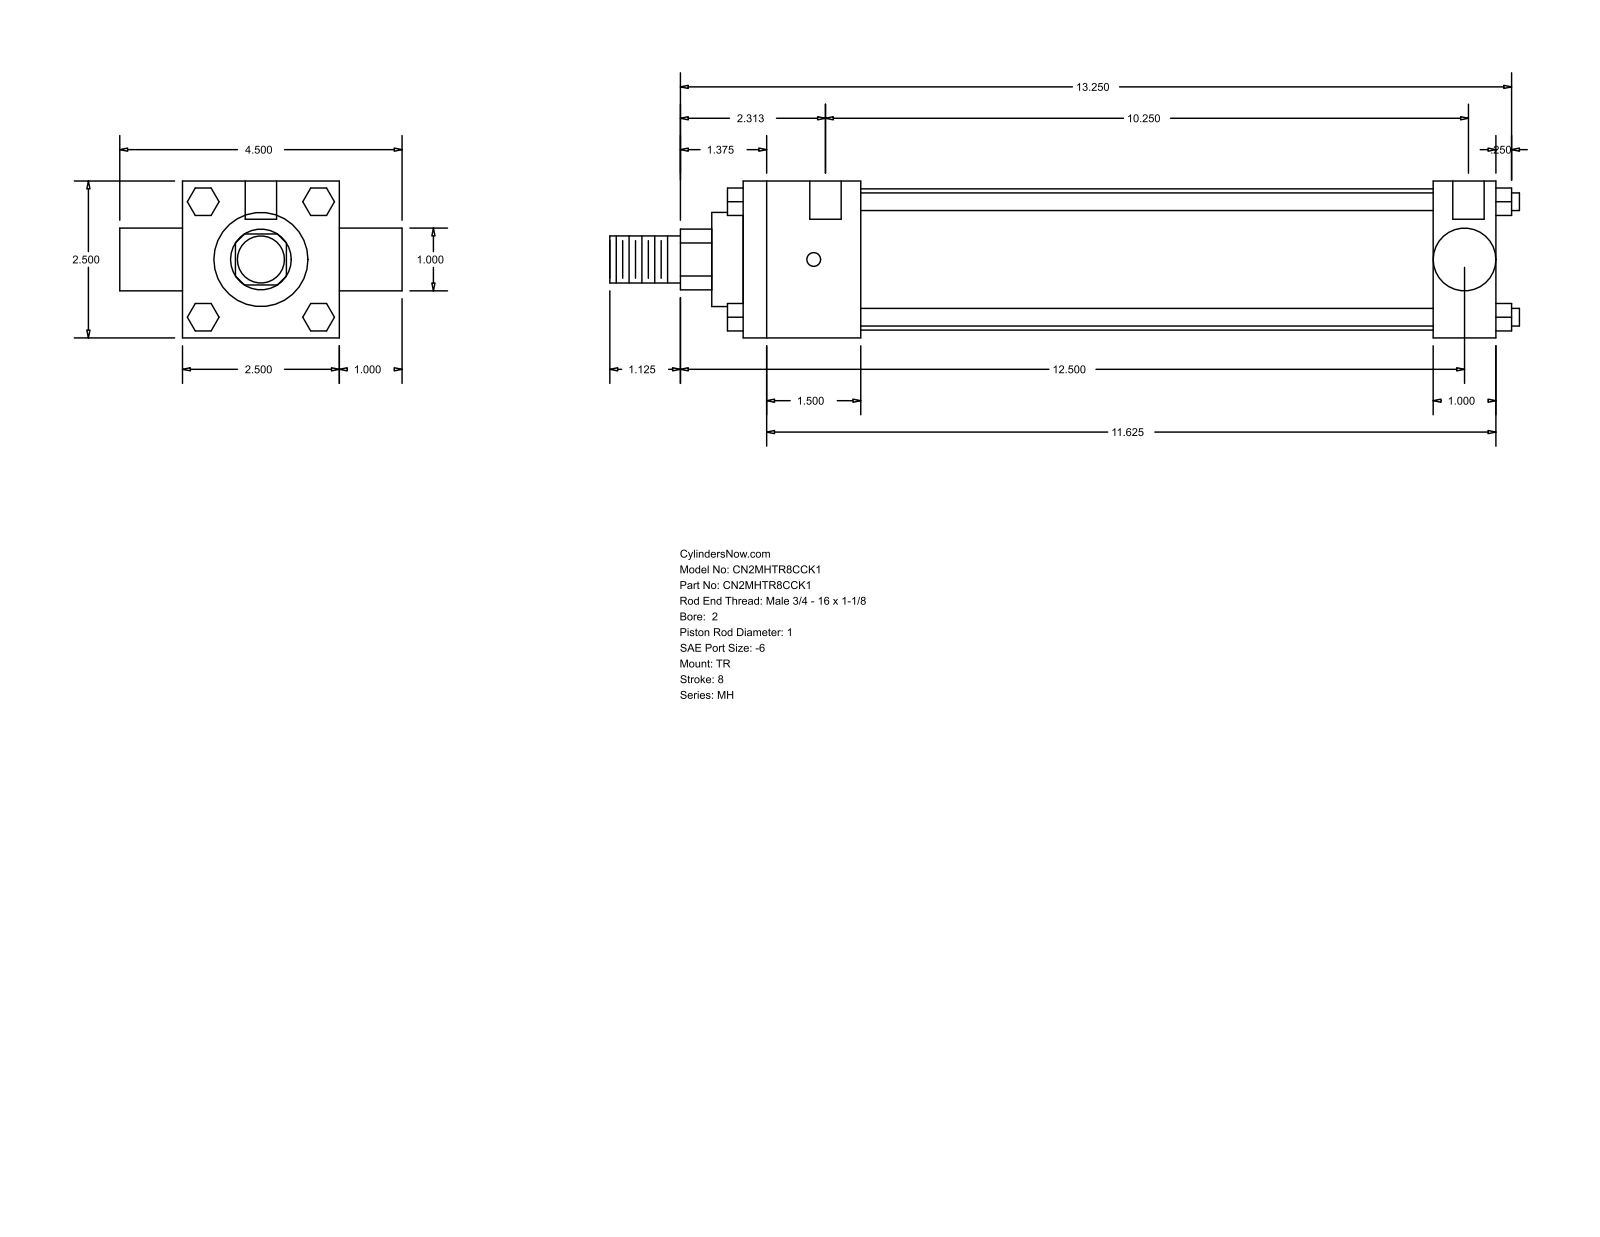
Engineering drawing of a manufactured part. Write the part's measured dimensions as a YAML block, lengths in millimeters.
part_name: "MH_TR__0200_1"
step_written_by: "GSSL Pune (CONFIG_CONTROL_DESIGN)"
units: millimeters
bodies: {solids: 0, faces: 120, planar: 92, cylindrical: 28, other: 0}
overall_size: [368.3, 114.3, 63.5]
round_holes:
  - {diameter: 5.56, count: 3}
  - {diameter: 12.7, count: 2}
round_bosses_or_shafts:
  - {diameter: 7.14, count: 4}
  - {diameter: 57.15, count: 1}
  - {diameter: 38.1, count: 1}
  - {diameter: 25.4, count: 1}
  - {diameter: 25.35, count: 1}
  - {diameter: 19.05, count: 1}
partial_cylinders:
  - {radius: 12.29, count: 1}
face_to_face_distances: [63.5, 304.8, 25.4, 47.63, 279.4, 231.77, 257.17, 88.9, 317.5, 6.35]
hole_center_spacings: [3.17, 4.76, 260.35, 263.52, 265.11, 268.28]
